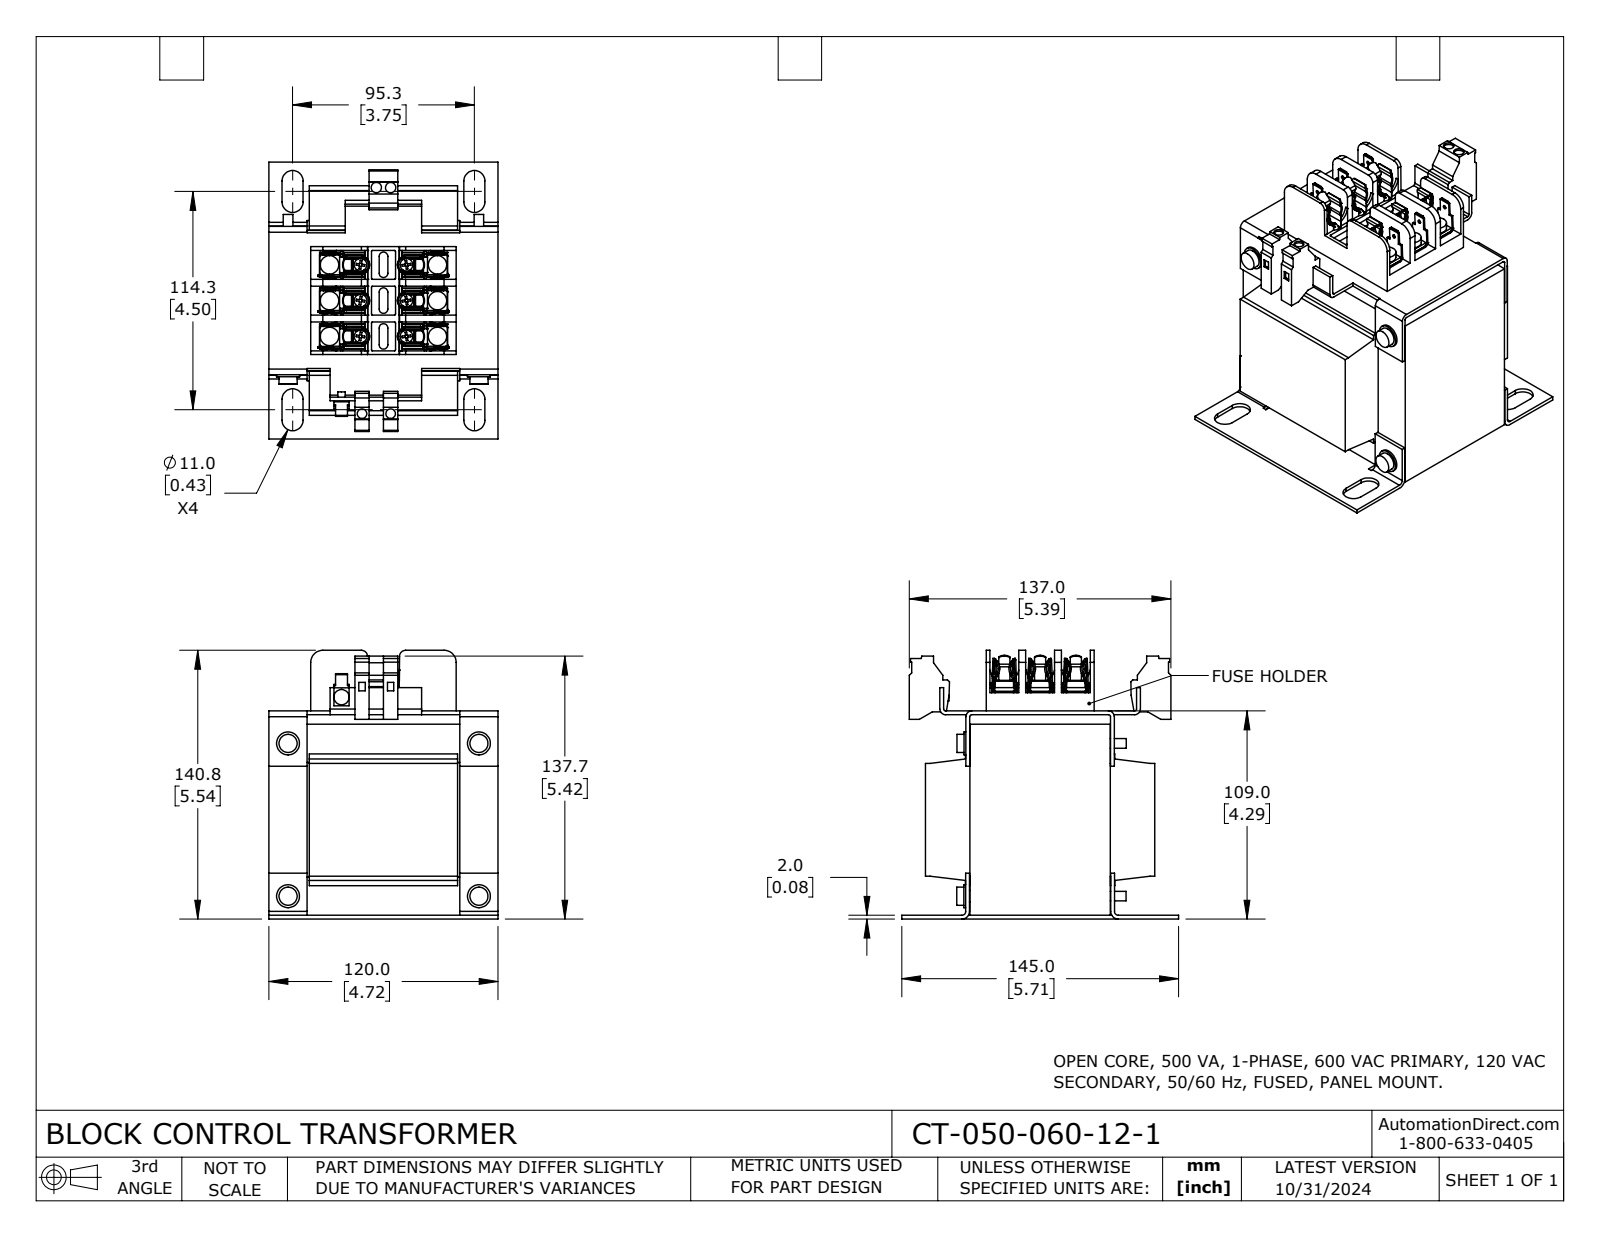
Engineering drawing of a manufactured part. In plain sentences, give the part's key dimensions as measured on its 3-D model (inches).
The part is named "CT-050-060-12-1". Its 3-D file was written by "SolidWorks 2023 (CONFIG_CONTROL_DESIGN)". It is 2 solids with 1583 faces: 1029 planar, 524 cylindrical and 30 other. Overall it measures 5.709 by 5.541 by 4.724 inches. Its volume is 75.15 cubic inches and its surface area 300.3 square inches. Round holes: 12 of diameter 0.074, 5 of diameter 0.205, 2 of diameter 0.197, 2 of diameter 0.213, 1 of diameter 0.205. Round bosses or shafts: 6 of diameter 0.38, 6 of diameter 0.19, 4 of diameter 0.472, 4 of diameter 0.374, 4 of diameter 0.236, 4 of diameter 0.197, 1 of diameter 0.315, 1 of diameter 0.157. Partial cylindrical surfaces (rounded edges, fillets, slot ends): 24 of radius 0.01, 20 of radius 0.05, 18 of radius 0.03, 14 of radius 0.072, 12 of radius 0.038, 12 of radius 0.04, 12 of radius 0.164, 9 of radius 0.097. The main face-to-face distances are 0.079, 4.213, 3.937, 0.787, 0.833, 3.892, 4.291, 3.15, 4.134, 0.197. The hole center spacings are 2.232, 2.354, 0.026, 0.026, 0.052, 0.738, 2.345, 1.863.
